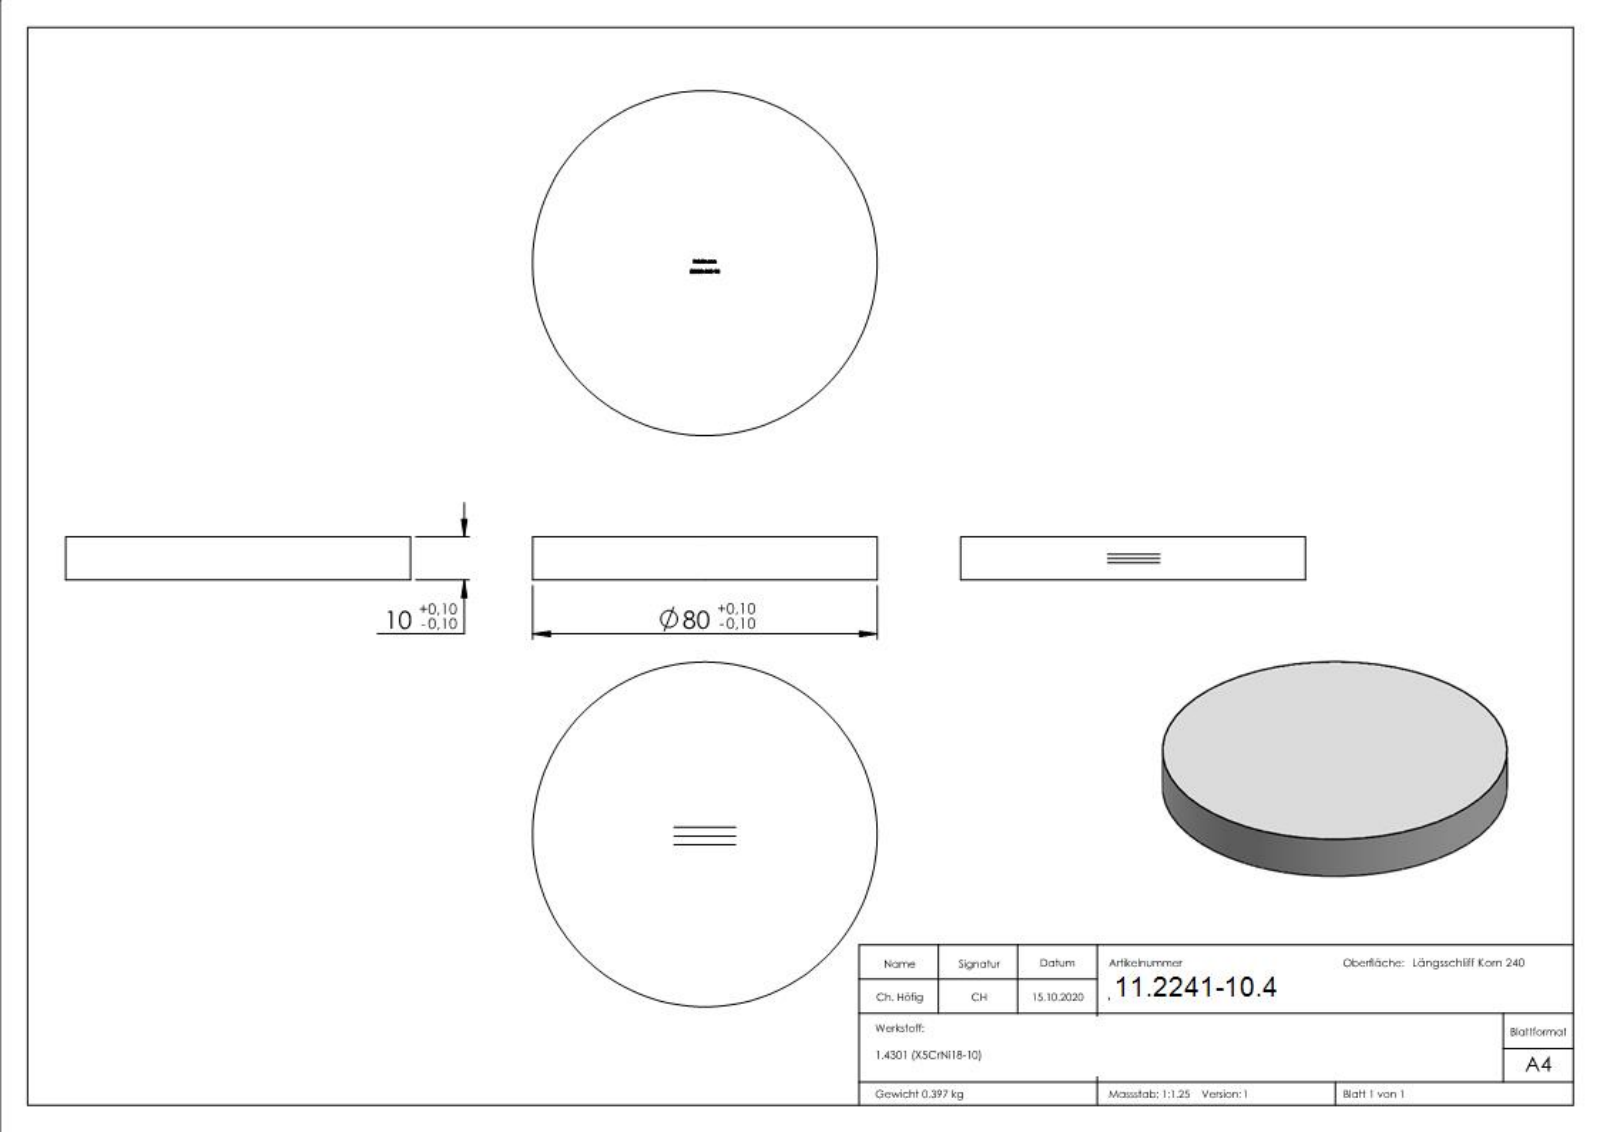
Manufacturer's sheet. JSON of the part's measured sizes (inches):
{"part_name": "53080-240-10", "step_written_by": "SolidWorks 2018 (CONFIG_CONTROL_DESIGN)", "units": "inches", "bodies": {"solids": 1, "faces": 259, "planar": 128, "cylindrical": 2, "other": 129}, "overall_size": [3.15, 3.15, 0.394], "volume_in3": 3.067, "surface_area_in2": 19.49, "round_bosses_or_shafts": [[3.15, 1]], "face_to_face_distances": [0.394, 0.39, 0.096, 0.039, 0.042, 0.07, 0.015, 0.033, 0.109, 0.094]}
